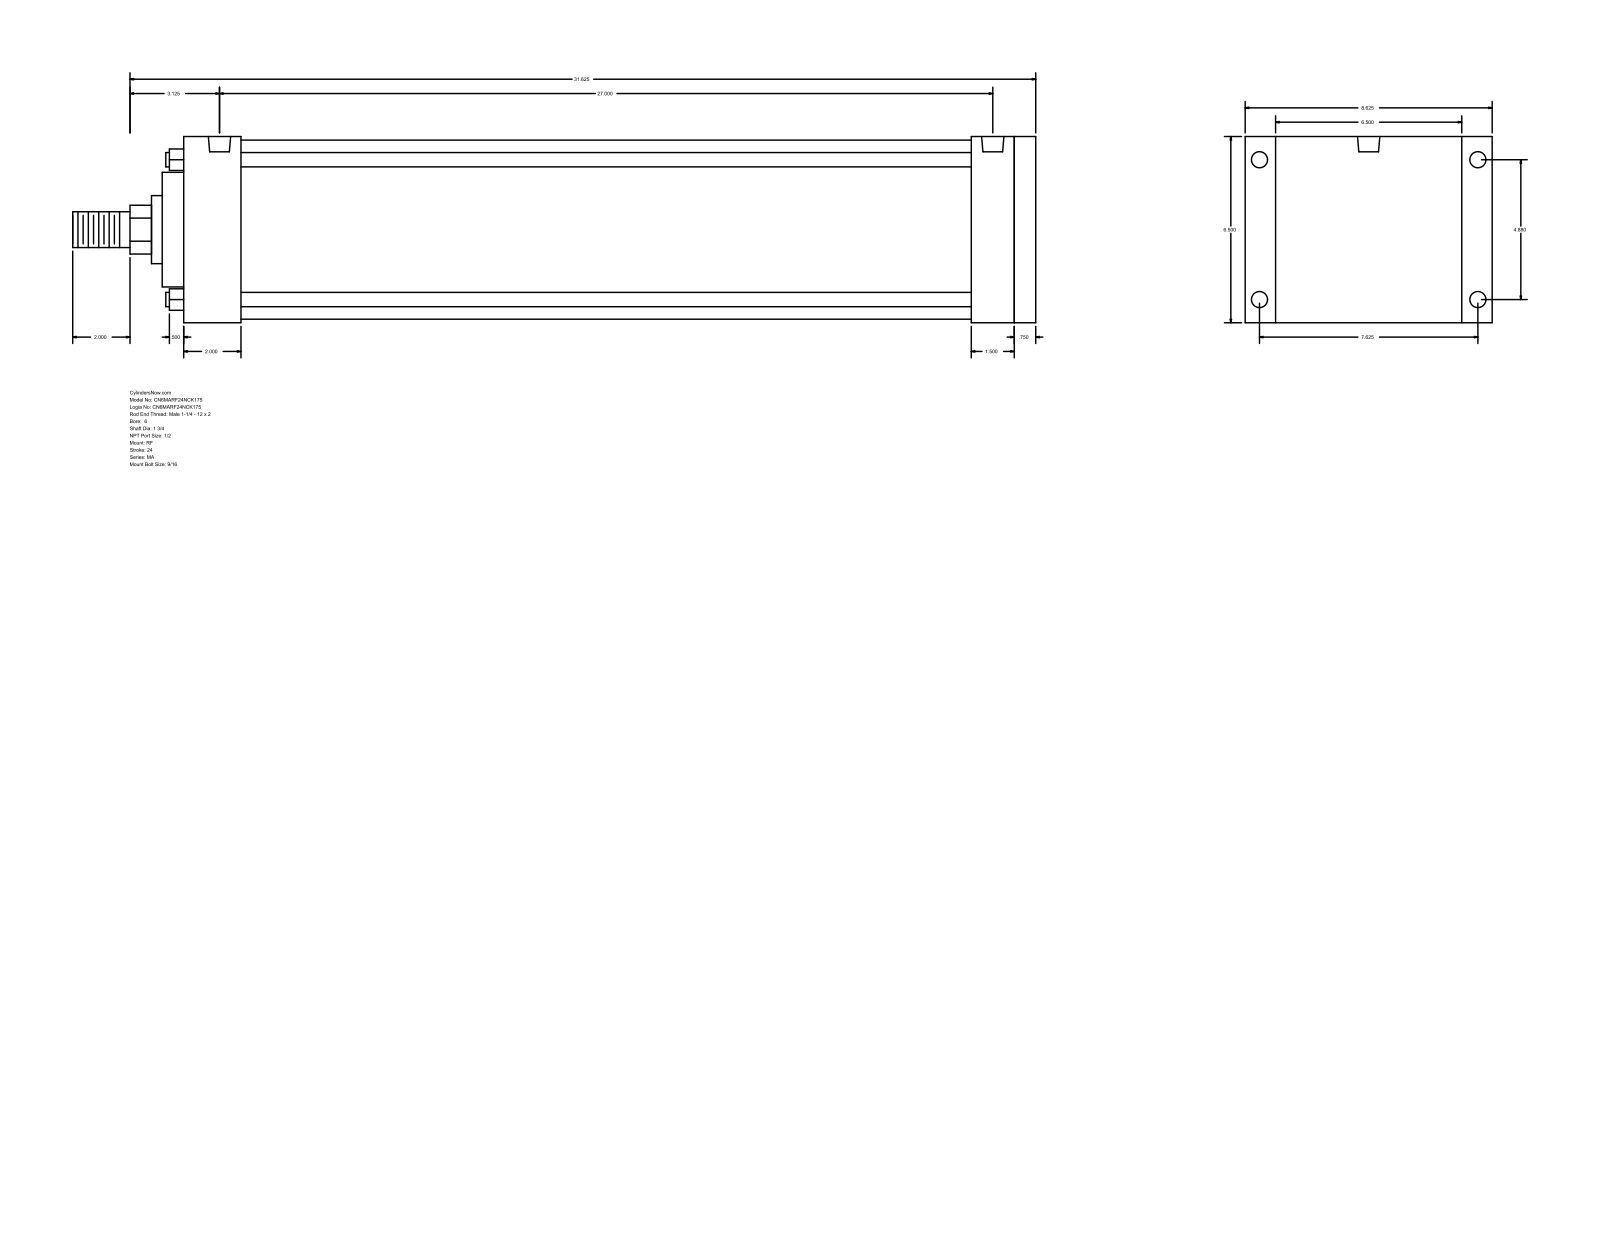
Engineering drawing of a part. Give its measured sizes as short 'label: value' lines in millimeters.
name: MA_RF__0600_1.75
written by: GSSL Pune (CONFIG_CONTROL_DESIGN)
unit: mm
bodies: 0 solids, 94 faces (65 planar, 29 cylindrical, 0 other)
size: 854.08 × 219.07 × 165.1
holes: 4× ⌀14.29, 4× ⌀17.46, 2× ⌀19.77
bosses: 4× ⌀12.7, 1× ⌀158.75, 1× ⌀101.6, 1× ⌀60.33, 1× ⌀44.45, 1× ⌀31.75
rounds: 1× R21.63
face distances: 165.1, 755.65, 19.04, 736.61, 50.8, 19.05, 685.81, 704.85, 698.5, 647.7
hole spacings: 123.96, 193.68, 229.95, 685.79
